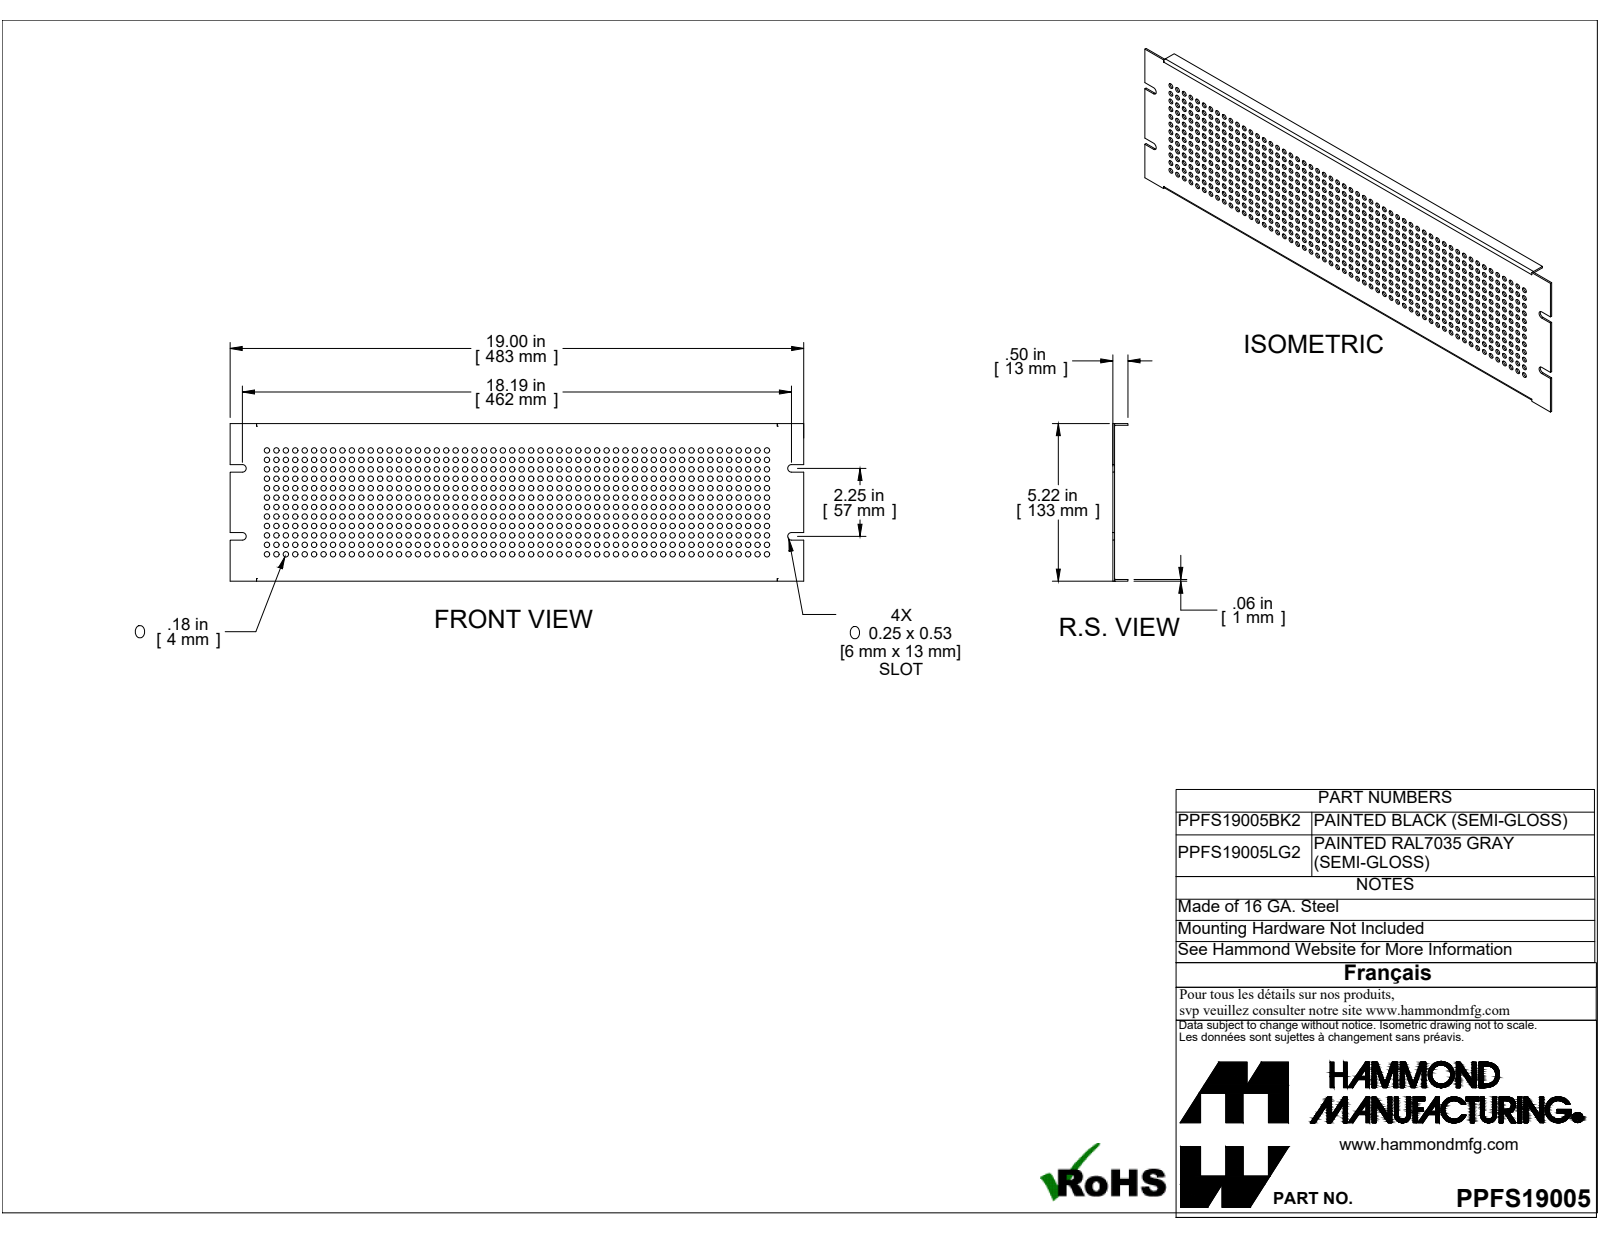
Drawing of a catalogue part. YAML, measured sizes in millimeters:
part_name: "PPFS19005BK2"
step_written_by: "SolidWorks 2019 (CONFIG_CONTROL_DESIGN)"
units: millimeters
bodies: {solids: 1, faces: 694, planar: 38, cylindrical: 656, other: 0}
overall_size: [482.6, 132.5, 12.7]
volume: 90720
surface_area: 140600
round_holes:
  - {diameter: 4.5, count: 648}
partial_cylinders:
  - {radius: 3.2, count: 4}
  - {radius: 0.7, count: 2}
  - {radius: 2.2, count: 2}
face_to_face_distances: [1.4, 131.1, 132.5, 129.6, 12.7, 11.3, 482.6, 22.2, 460.4, 40.9]
hole_center_spacings: [17.8, 8, 32.7, 11.2, 25.1, 31.8, 7.9, 15.9]
